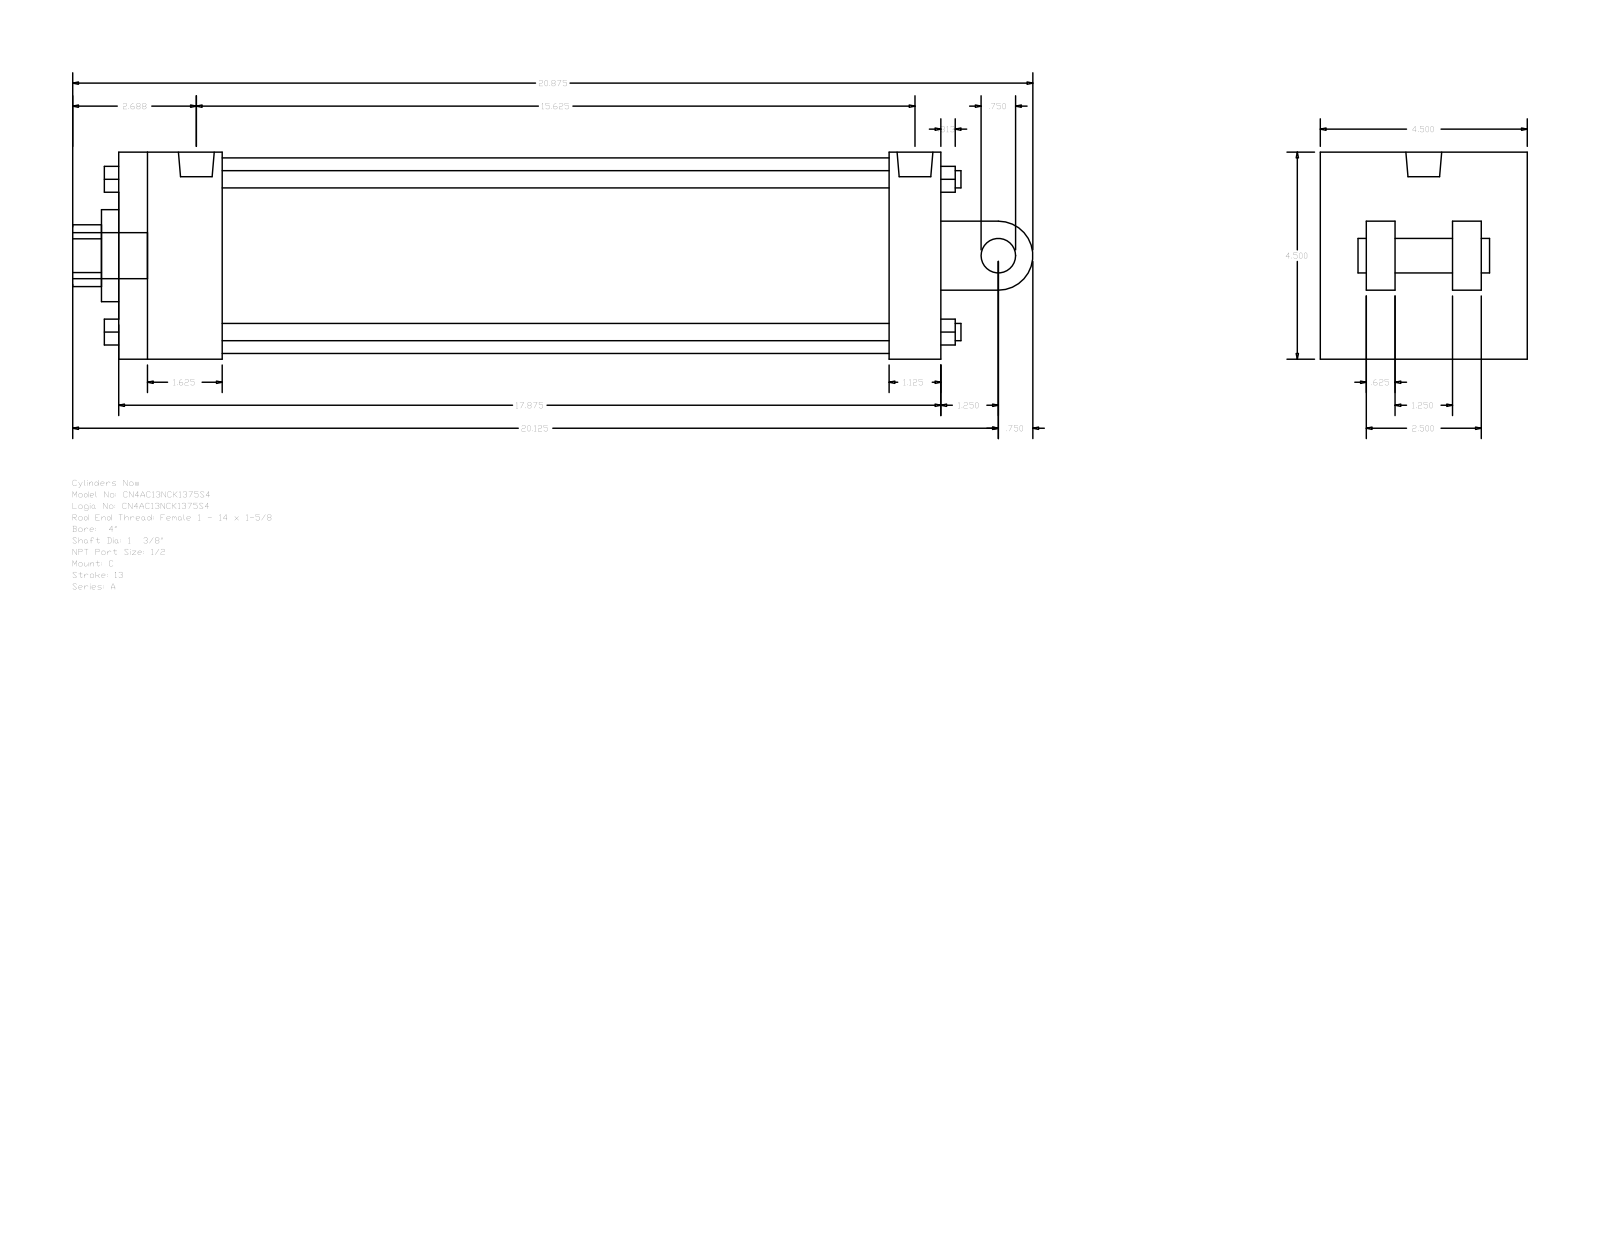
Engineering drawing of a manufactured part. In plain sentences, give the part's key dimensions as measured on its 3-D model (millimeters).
The part is named "A_C__0400_1.375". Its 3-D file was written by "GSSL Pune (CONFIG_CONTROL_DESIGN)". It is 0 solids with 135 faces: 102 planar, 33 cylindrical and 0 other. Overall it measures 530.23 by 114.3 by 114.3 millimeters. Round holes: 2 of diameter 8.73, 1 of diameter 19.77, 1 of diameter 34.92, 1 of diameter 50.8, 1 of diameter 107.95. Round bosses or shafts: 4 of diameter 9.53, 2 of diameter 8.73, 1 of diameter 25.4, 1 of diameter 19.77, 1 of diameter 19.05. Partial cylindrical surfaces (rounded edges, fillets, slot ends): 1 of radius 17.06, 1 of radius 19.05. The main face-to-face distances are 114.3, 454.03, 28.58, 73.03, 425.45, 57.15, 368.3, 396.88, 15.87, 25.4. The hole center spacings are 3.18.
